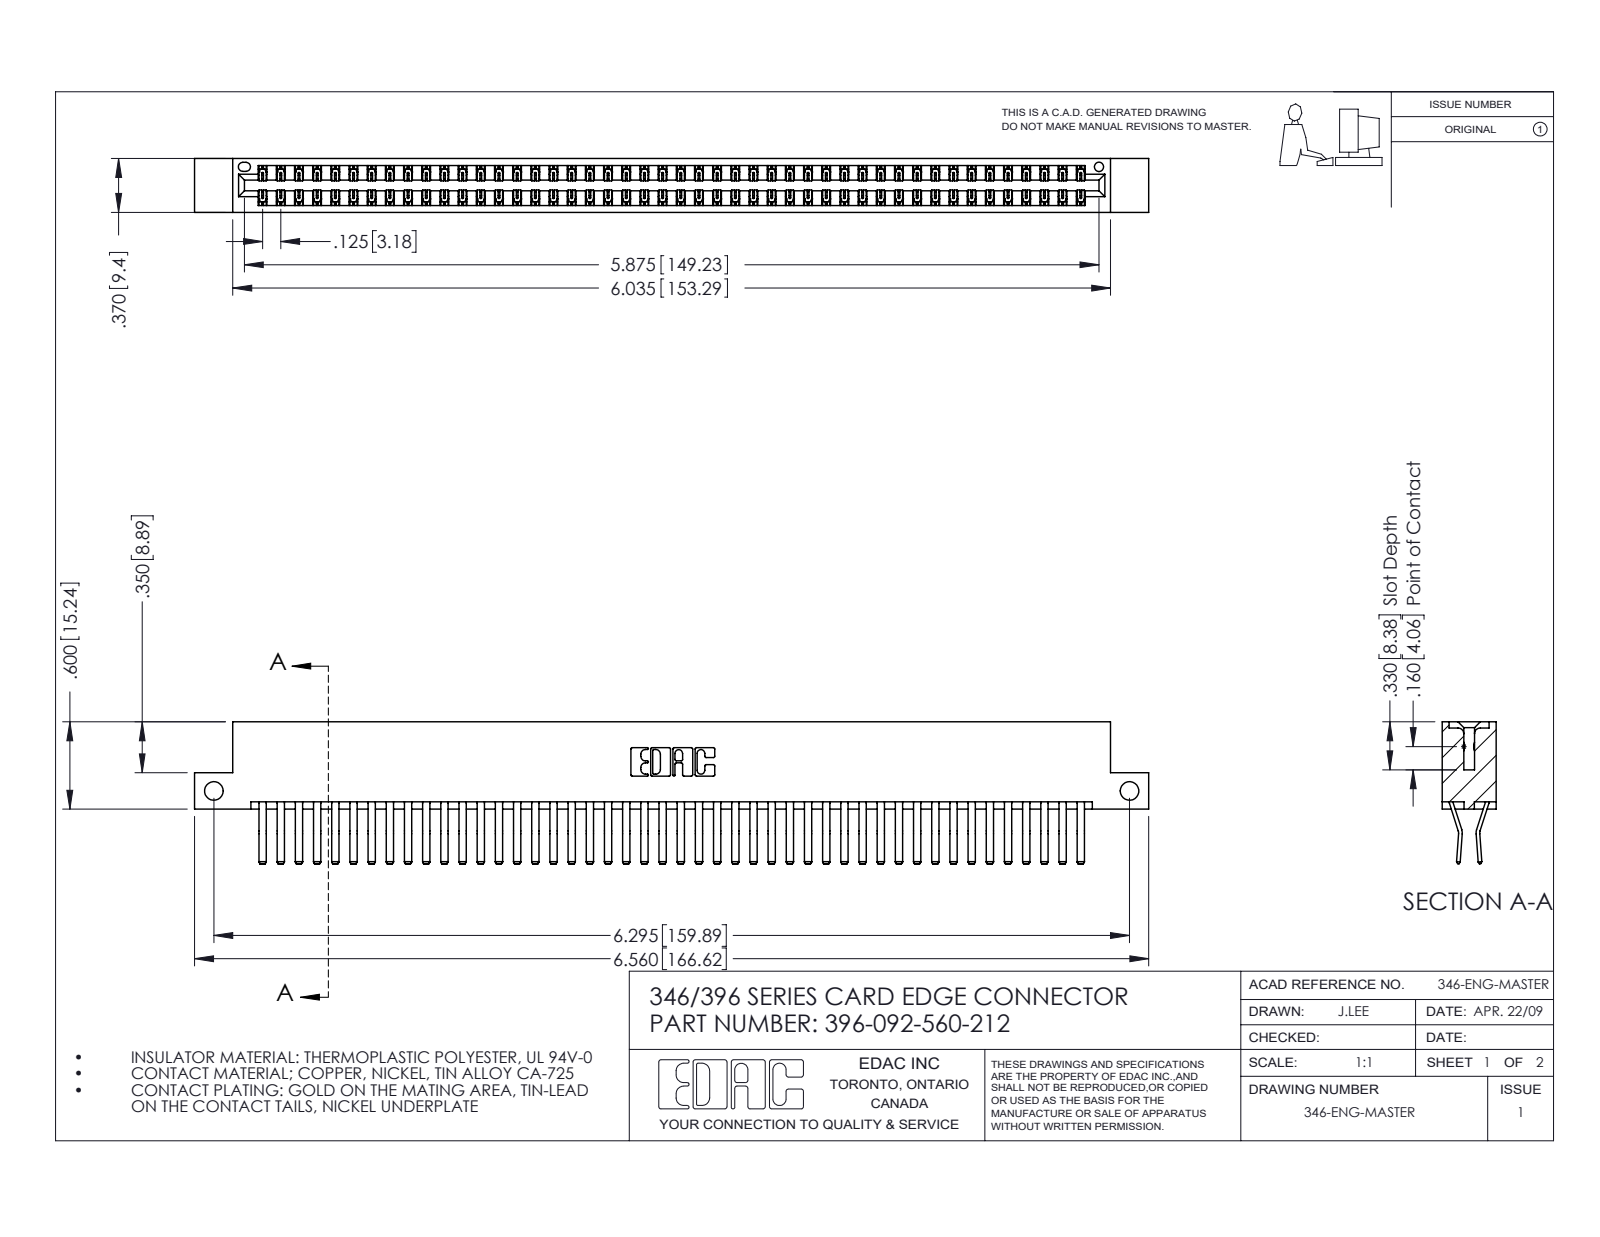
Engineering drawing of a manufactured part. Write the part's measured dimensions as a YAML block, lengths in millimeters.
part_name: "396-092-560-212; 345-292-001_560 Tail; 346 Part_Flush Mounting Lugs - Side Mount"
step_written_by: "SolidWorks 2016 (CONFIG_CONTROL_DESIGN)"
units: millimeters
bodies: {solids: 93, faces: 5090, planar: 3296, cylindrical: 1794, other: 0}
overall_size: [166.6, 24.8, 9.4]
volume: 16800
surface_area: 24620
round_holes:
  - {diameter: 3.3, count: 2}
  - {diameter: 1.6, count: 1}
partial_cylinders:
  - {radius: 0.2, count: 138}
  - {radius: 0.3, count: 22}
  - {radius: 0.2, count: 6}
  - {radius: 0.8, count: 6}
  - {radius: 0.7, count: 3}
  - {radius: 0.3, count: 2}
  - {radius: 0.4, count: 2}
  - {radius: 0.6, count: 2}
face_to_face_distances: [1.2, 8.2, 9.4, 0.6, 6.4, 1.8, 7.6, 7, 3.8, 5.6]
hole_center_spacings: [159.9]
